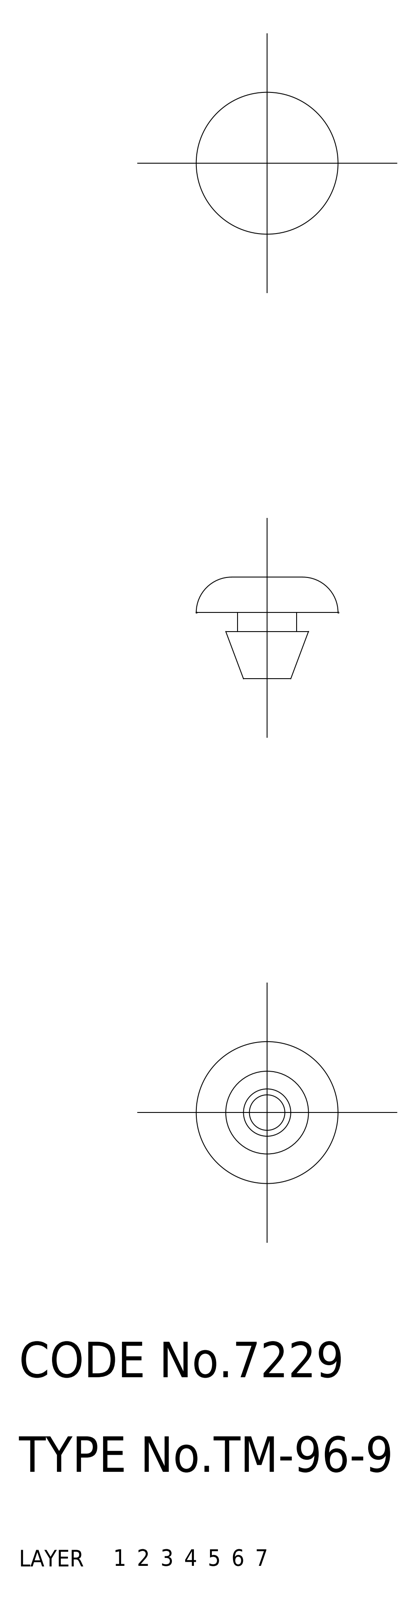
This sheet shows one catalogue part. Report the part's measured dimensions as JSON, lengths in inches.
{"part_name": "cushion", "step_written_by": "CADfix (AUTOMOTIVE_DESIGN)", "units": "inches", "bodies": {"solids": 1, "faces": 13, "planar": 0, "cylindrical": 0, "other": 13}, "overall_size": [0.472, 0.472, 0.339], "volume_in3": 0.022, "surface_area_in2": 0.698}
